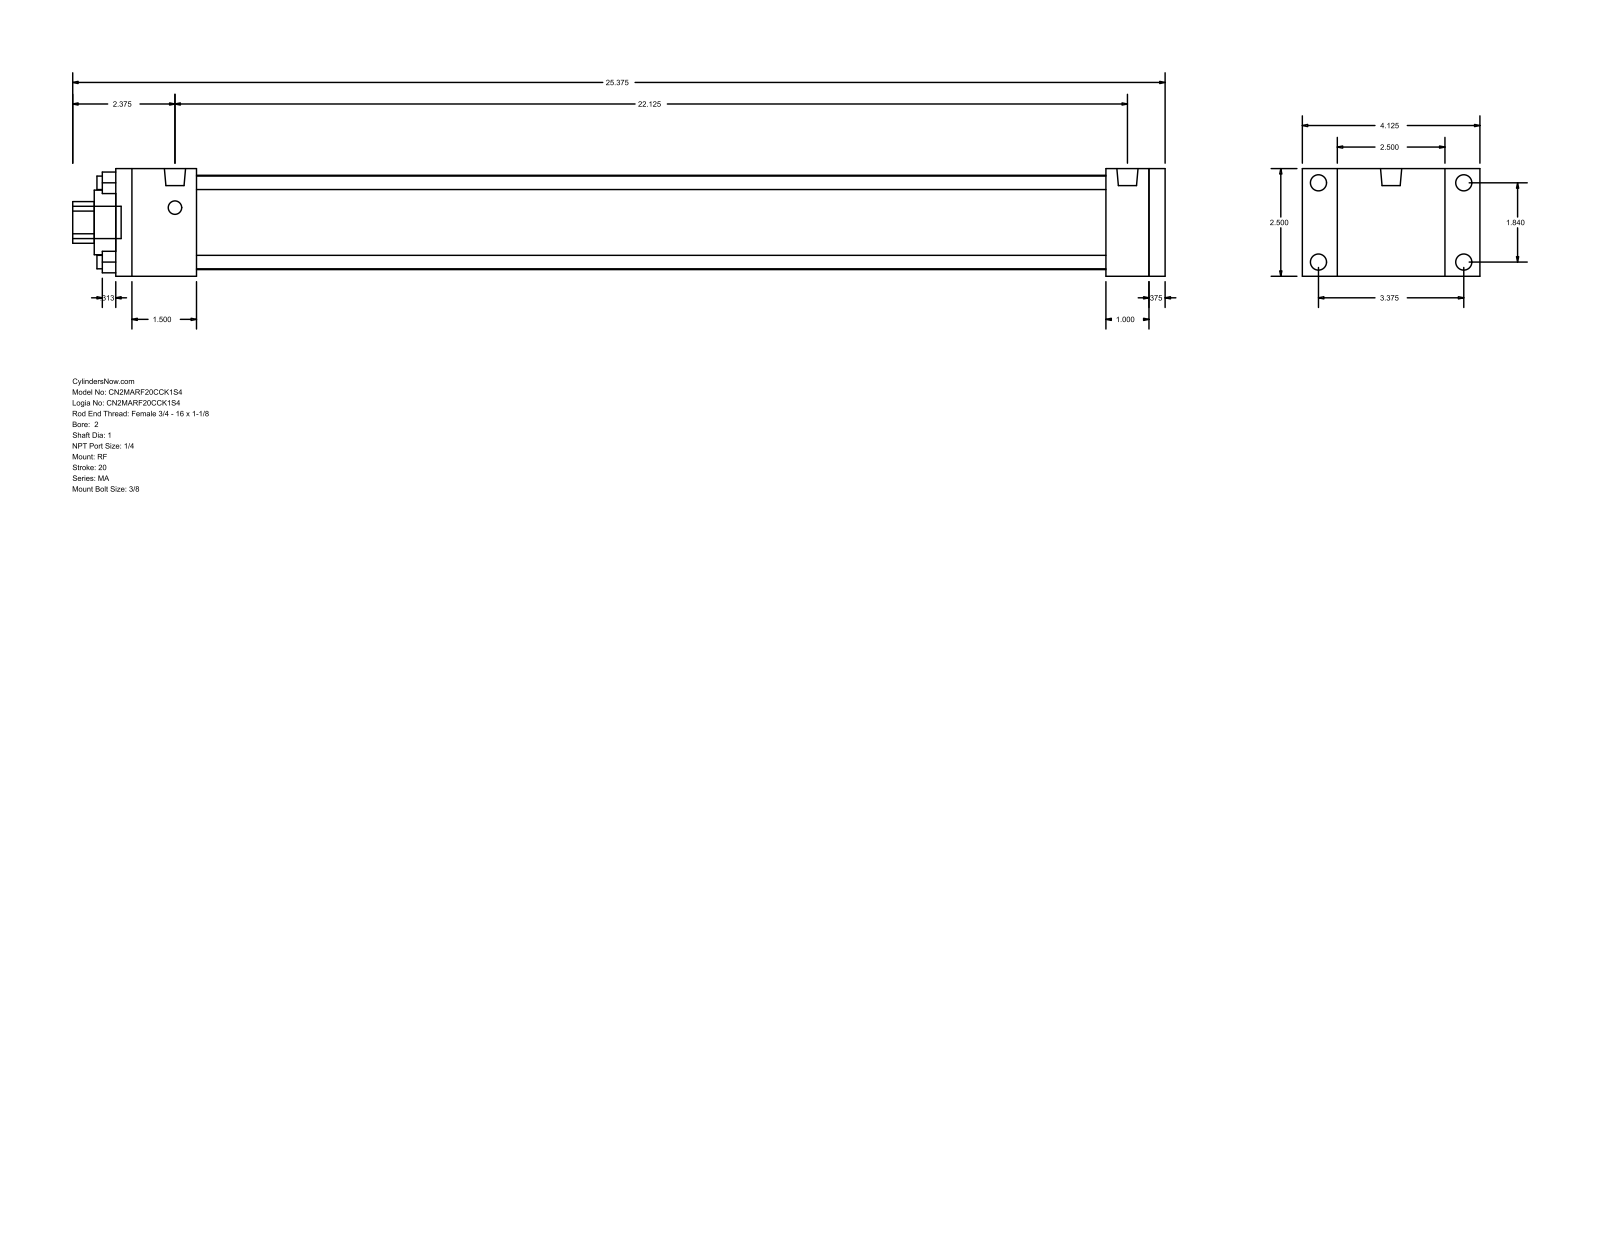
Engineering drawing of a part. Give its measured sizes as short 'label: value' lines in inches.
name: MA_RF__0200_1
written by: GSSL Pune (CONFIG_CONTROL_DESIGN)
unit: in
bodies: 0 solids, 92 faces (64 planar, 28 cylindrical, 0 other)
size: 25.375 × 4.125 × 2.5
holes: 4× ⌀0.313, 1× ⌀1, 1× ⌀1.5, 1× ⌀2.19
bosses: 4× ⌀0.375, 4× ⌀0.313, 2× ⌀0.492, 1× ⌀0.75
rounds: 1× R0.484
face distances: 2.5, 24, 0.375, 24.375, 1, 0.813, 0.5, 1.875, 22.125, 22.5
hole spacings: 1.301, 1.84, 2.602
